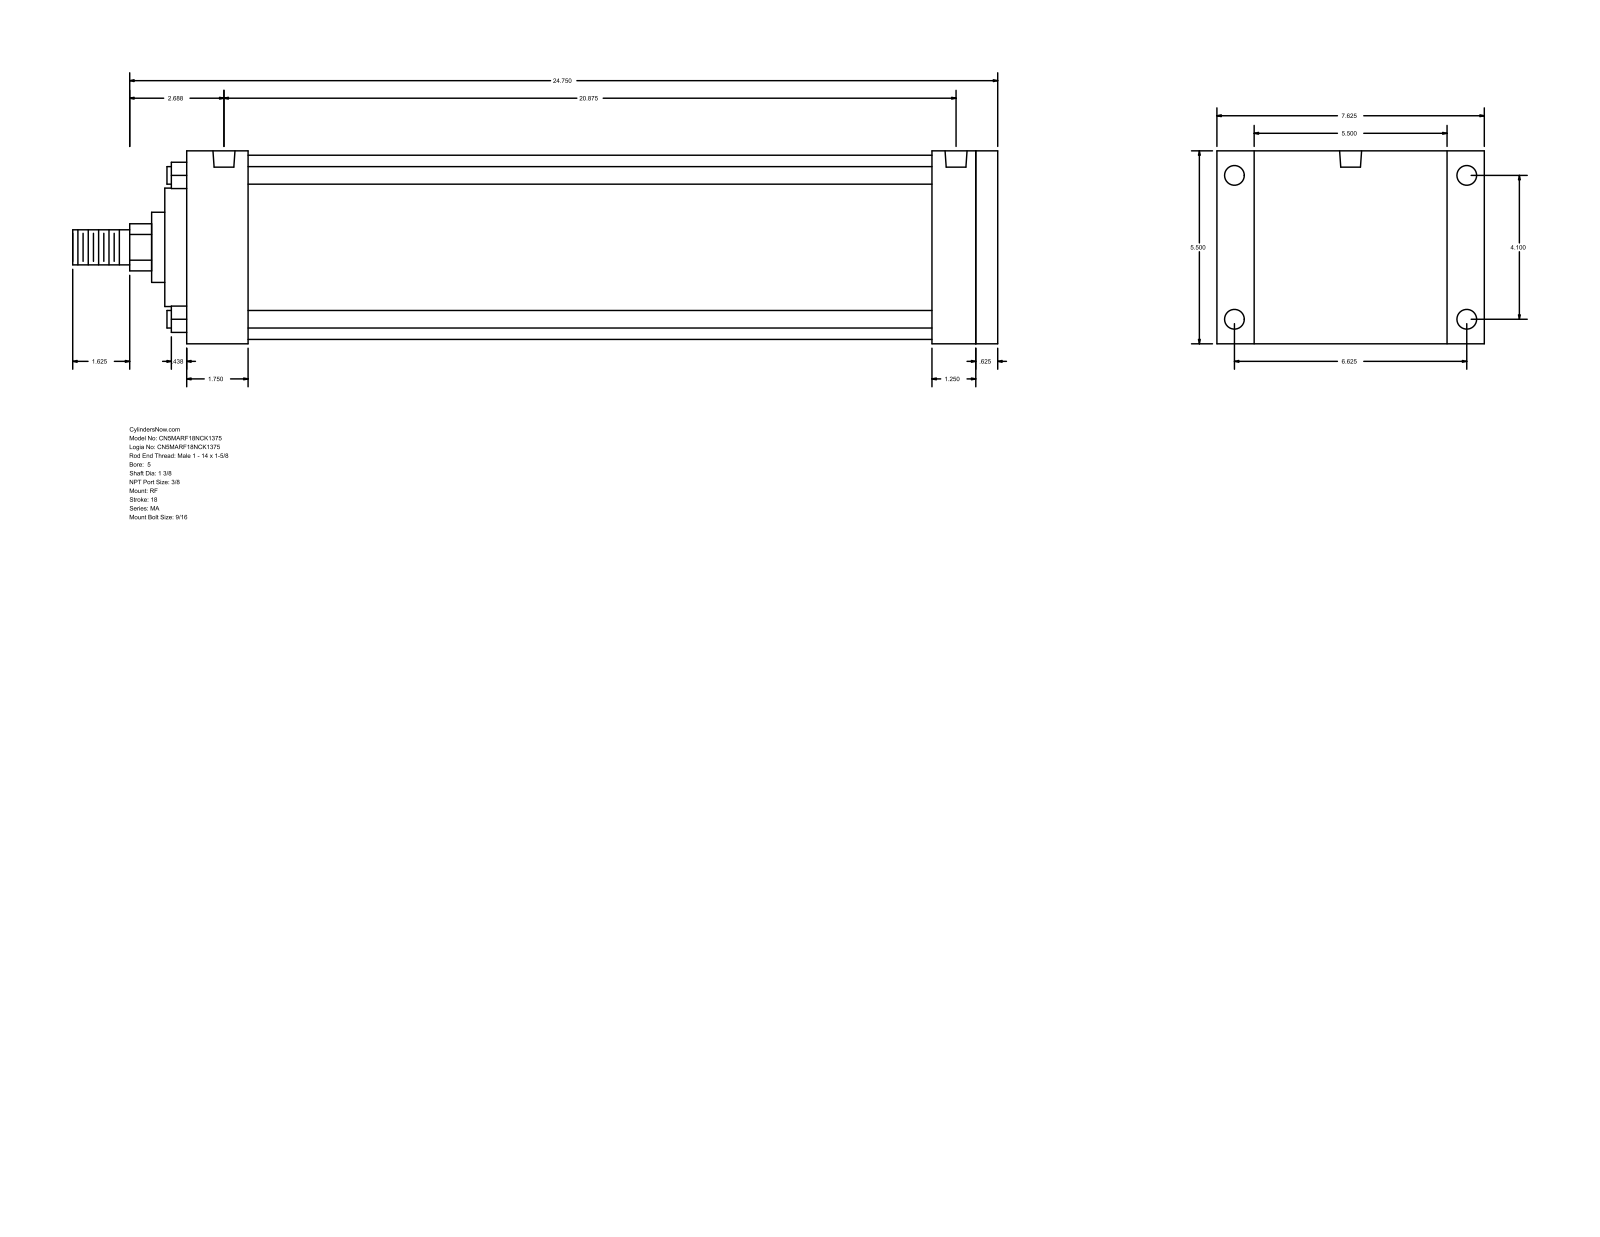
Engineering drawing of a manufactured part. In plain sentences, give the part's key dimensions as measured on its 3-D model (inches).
The part is named "MA_RF__0500_1.375". Its 3-D file was written by "GSSL Pune (CONFIG_CONTROL_DESIGN)". It is 0 solids with 94 faces: 65 planar, 29 cylindrical and 0 other. Overall it measures 26.375 by 7.625 by 5.5 inches. Round holes: 4 of diameter 0.437, 4 of diameter 0.563, 2 of diameter 0.627. Round bosses or shafts: 4 of diameter 0.5, 1 of diameter 5.25, 1 of diameter 3.375, 1 of diameter 2, 1 of diameter 1.375, 1 of diameter 1. Partial cylindrical surfaces (rounded edges, fillets, slot ends): 1 of radius 0.672. The main face-to-face distances are 5.5, 23.125, 0.625, 22.5, 1.75, 20.75, 21.375, 21.25, 19.5, 1.25. The hole center spacings are 4.1, 6.625, 7.791, 20.5, 0.187, 0.188, 20.687, 20.688.
